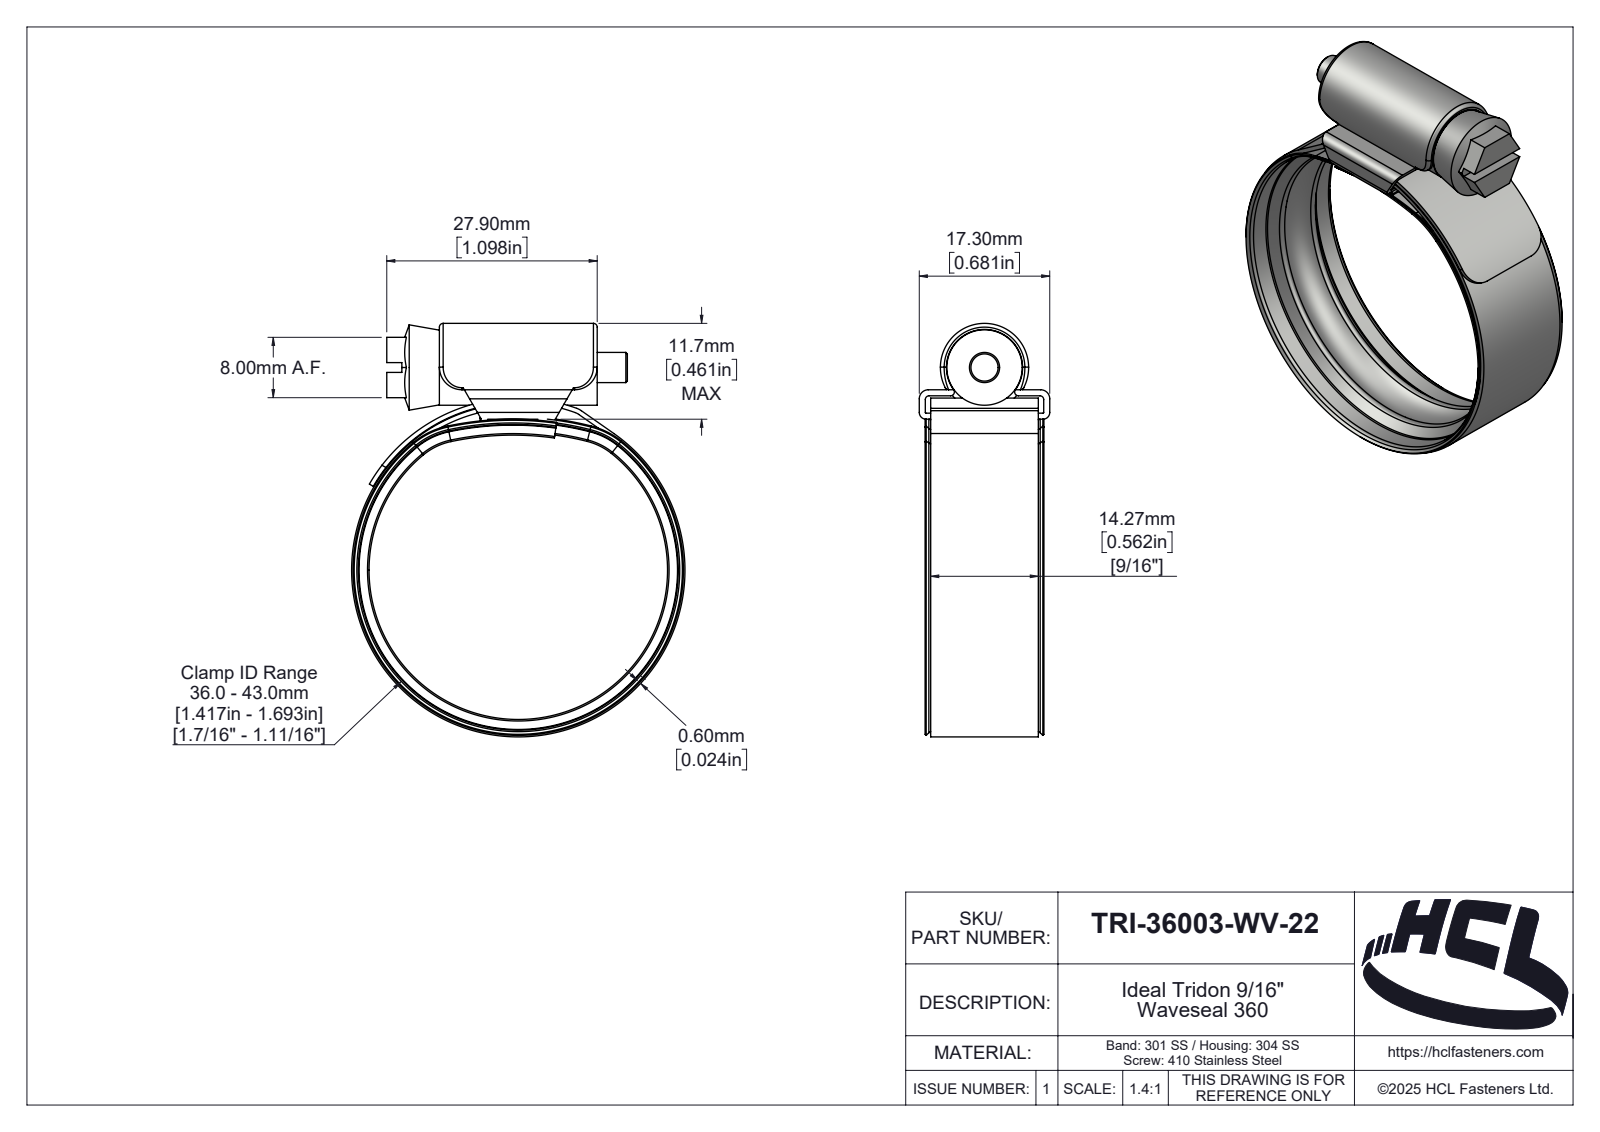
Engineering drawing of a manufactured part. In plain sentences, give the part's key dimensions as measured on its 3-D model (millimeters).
The part is named "TRI-36003-WV-22". Its 3-D file was written by "SolidWorks 2025 (AUTOMOTIVE_DESIGN)". It is 4 solids with 418 faces: 42 planar, 119 cylindrical and 257 other. Overall it measures 54.8 by 44.2 by 17.3 millimeters. Its volume is 4 723 cubic millimeters and its surface area 12 628 square millimeters. Round holes: 1 of diameter 43. Round bosses or shafts: 1 of diameter 44.2, 1 of diameter 10, 1 of diameter 4. Partial cylindrical surfaces (rounded edges, fillets, slot ends): 6 of radius 0.5, 4 of radius 3, 2 of radius 0.1, 2 of radius 0.9, 2 of radius 1.2, 2 of radius 9.9, 2 of radius 10.1, 1 of radius 0.46. The main face-to-face distances are 0.8, 3.1, 14.26, 2.3, 0.6, 3.9, 27.9, 1.52, 15.78, 16.5.
